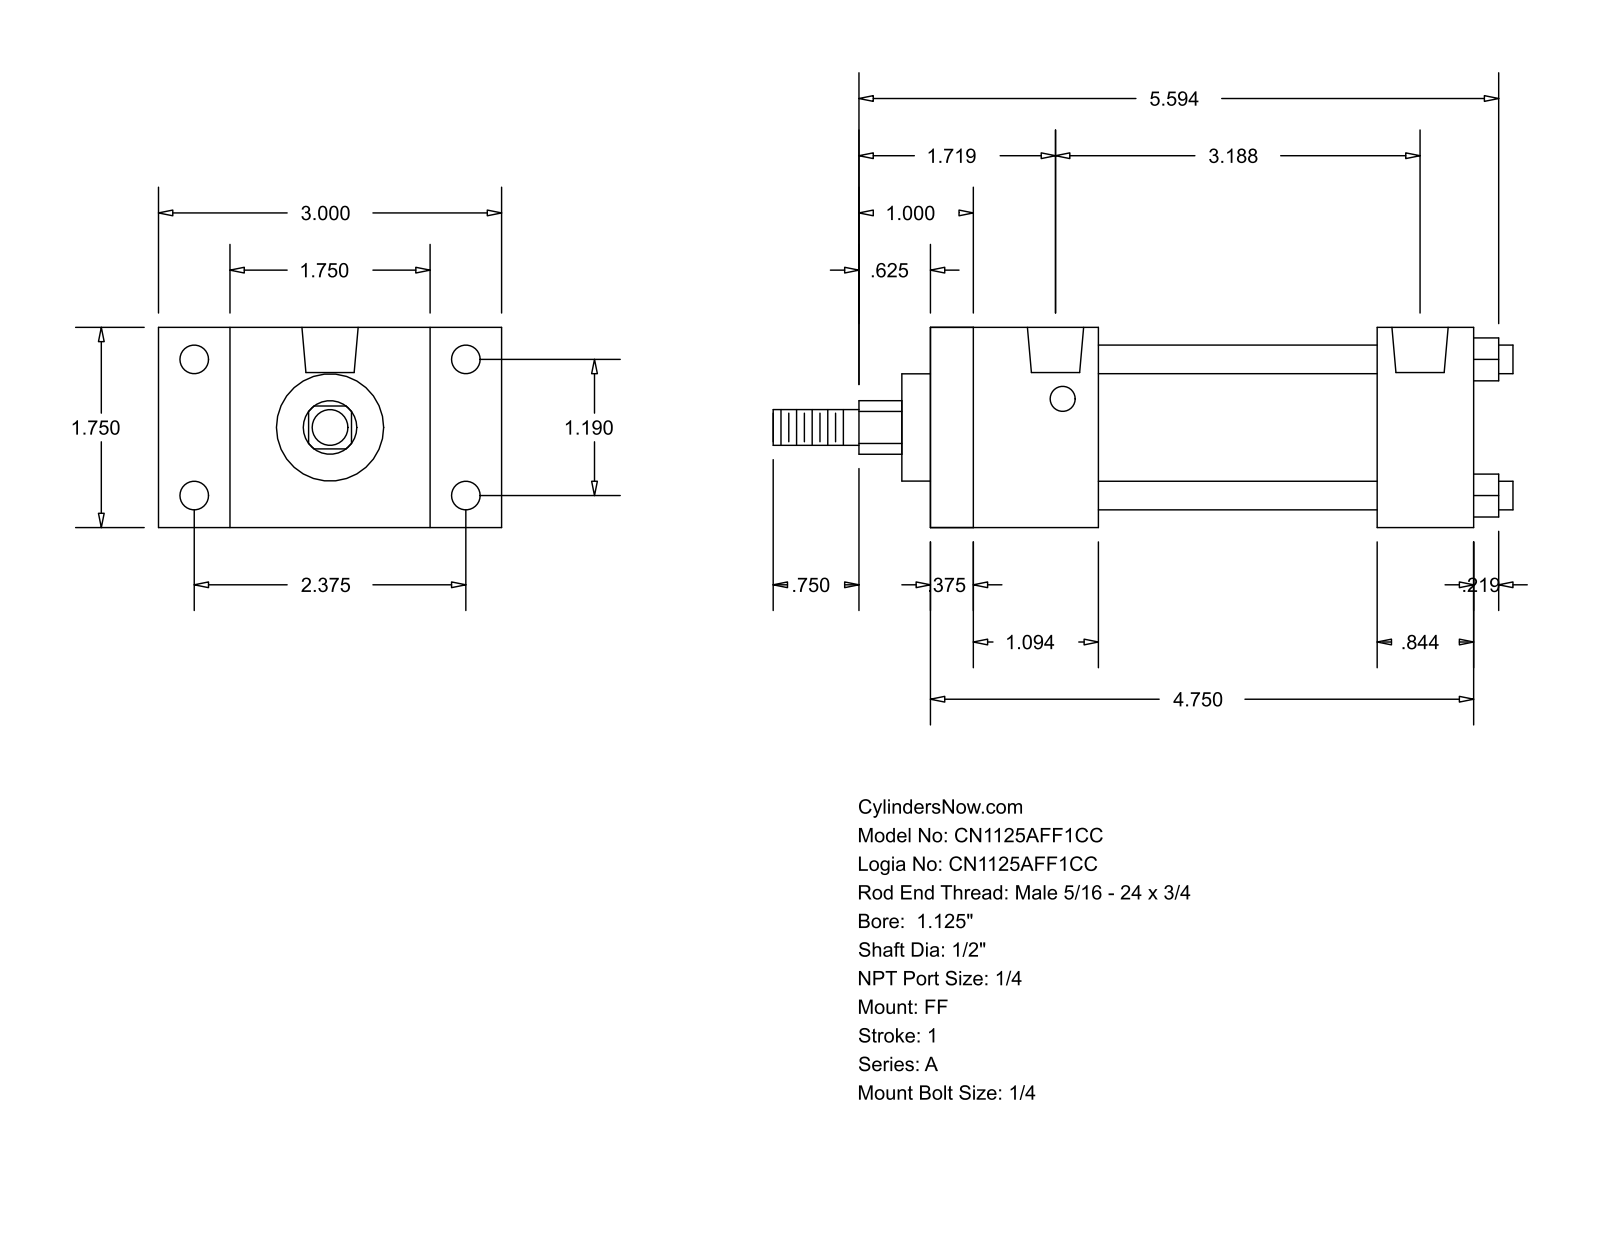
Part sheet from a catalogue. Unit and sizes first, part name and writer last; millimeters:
Units: millimetres
Overall size (bounding box): 164.31 × 76.2 × 44.45
Round holes (diameter × count): ⌀5.56 ×4, ⌀6.35 ×4, ⌀12.49 ×2
Round bosses / shafts (diameter × count): ⌀6.35 ×4, ⌀31.88 ×1, ⌀23.81 ×1, ⌀12.7 ×1, ⌀7.94 ×1
Partial cylindrical surfaces — rounded edges, fillets, slot ends (radius × count): R5.94 ×1
Main face-to-face distances: 44.46, 120.65, 9.52, 111.13, 15.87, 99.21, 89.69, 21.44, 37.3, 27.78
Hole centre spacings: 30.22, 60.32, 67.47, 77.79, 1.58, 1.59, 79.37, 79.38
Bodies: 0 solids, 92 faces (64 planar, 28 cylindrical, 0 other)
Part name (STEP PRODUCT): A_FF__0112_0.5
STEP written by: GSSL Pune (CONFIG_CONTROL_DESIGN)
